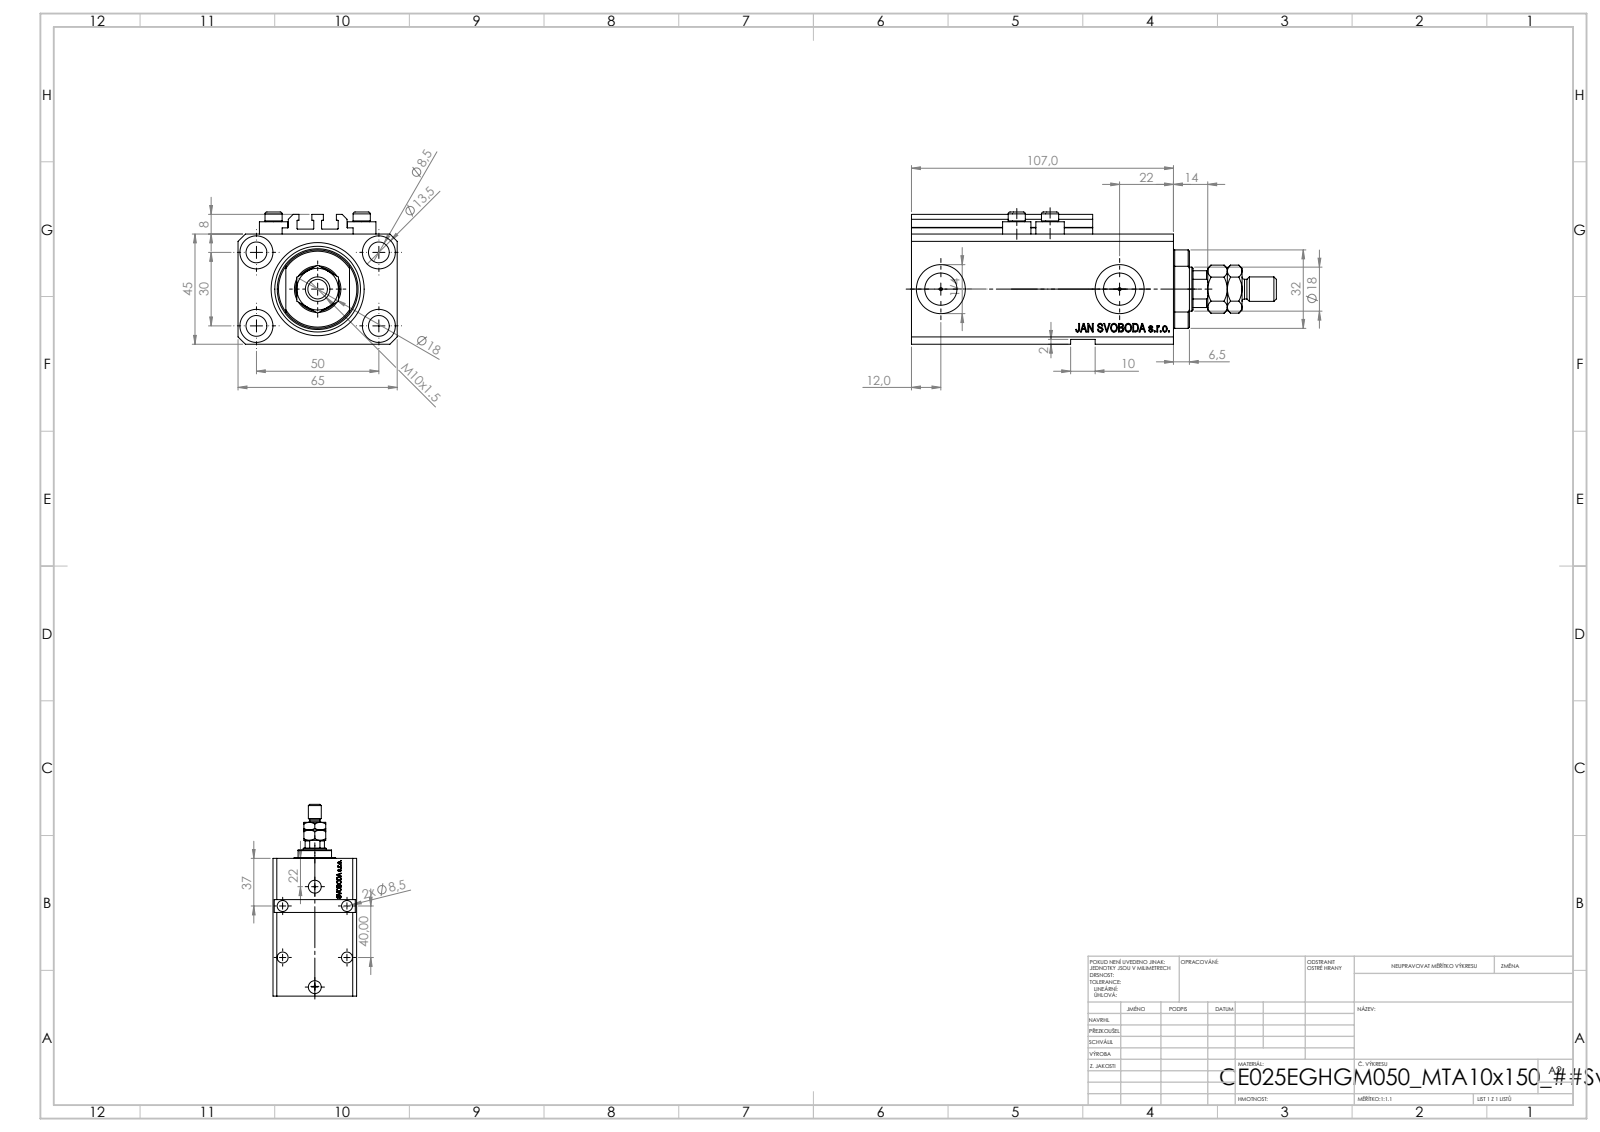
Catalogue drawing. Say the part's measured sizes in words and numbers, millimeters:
The part is named "V250CE_C_VCP; MTA; V250CE_E_Body; ALLEN BOLT V250CE (+1 more)". Its 3-D file was written by "SolidWorks 2019 (CONFIG_CONTROL_DESIGN)". It is 9 solids with 1136 faces: 526 planar, 150 cylindrical and 460 other. Overall it measures 149 by 65 by 54 millimeters. Its volume is 277 886 cubic millimeters and its surface area 78 614 square millimeters. Round holes: 9 of diameter 8.5, 4 of diameter 1.25, 4 of diameter 4, 4 of diameter 13.5, 2 of diameter 10, 2 of diameter 13.16, 2 of diameter 20, 1 of diameter 18, 1 of diameter 25, 1 of diameter 38. Round bosses or shafts: 4 of diameter 11.6, 4 of diameter 7, 1 of diameter 10, 1 of diameter 8. Partial cylindrical surfaces (rounded edges, fillets, slot ends): 10 of radius 0.2, 1 of radius 8.5, 1 of radius 16. The main face-to-face distances are 45, 65, 14, 93, 2, 47, 107, 6.9, 20.5, 2.5. The hole center spacings are 29.15, 50, 13.6, 14.76, 15.12, 27.51, 27.89, 30.
